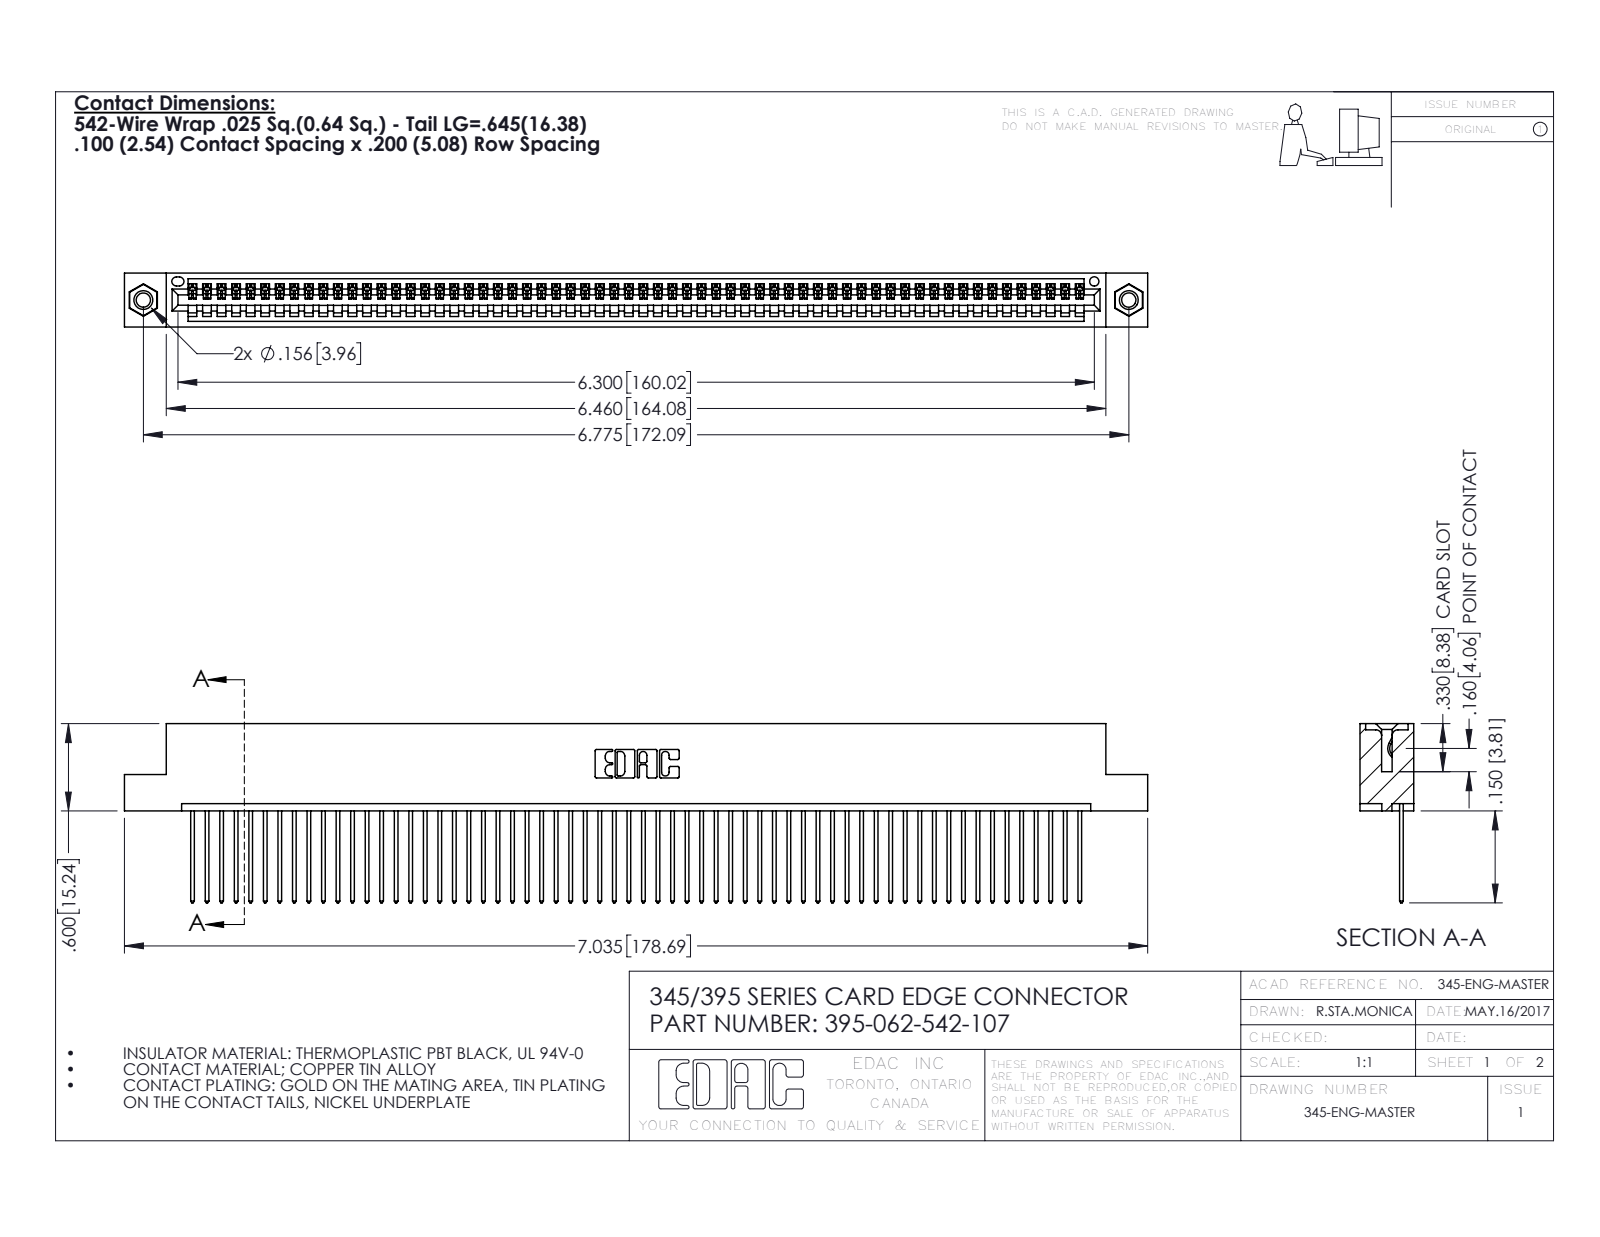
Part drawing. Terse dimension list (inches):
name: 395-062-542-107; 345-292-001_345-293-142; 345-250-001_345-250-005-103; 345 Part_Flush Mounting Lugs - 0.156 Dia-TI
written by: SolidWorks 2016 (CONFIG_CONTROL_DESIGN)
unit: in
bodies: 65 solids, 3782 faces (2592 planar, 1174 cylindrical, 16 other)
size: 7.035 × 1.232 × 0.37
volume: 1.053 in³; area: 37.38 in²
holes: 2× ⌀0.098, 2× ⌀0.125, 2× ⌀0.156, 1× ⌀0.064
bosses: 2× ⌀0.155
rounds: 124× R0.006, 124× R0.01, 22× R0.01, 6× R0.007, 6× R0.031, 3× R0.026, 2× R0.031, 2× R0.04
face distances: 0.072, 0.298, 0.098, 0.272, 0.025, 0.37, 0.2, 0.225, 0.149, 0.072
hole spacings: 0.27, 6.539, 6.775
